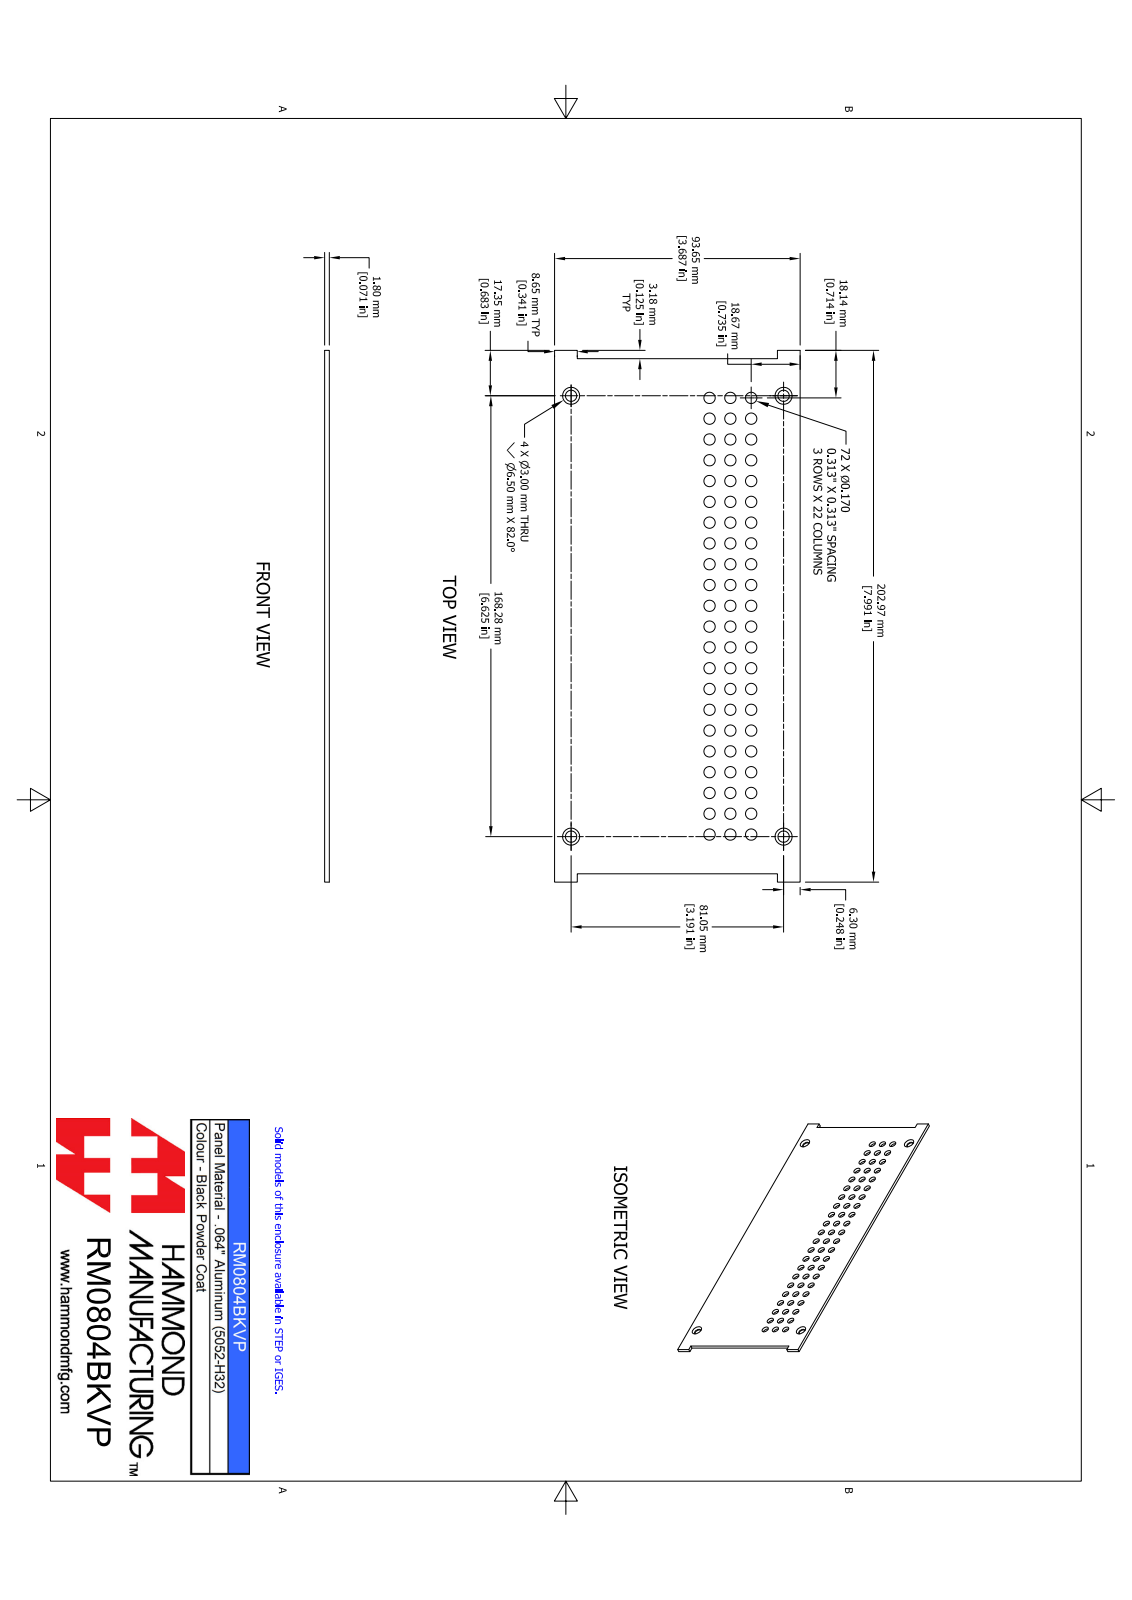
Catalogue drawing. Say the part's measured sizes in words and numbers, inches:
The part is named "RM0804BKVP". Its 3-D file was written by "SolidWorks 2021 (AUTOMOTIVE_DESIGN)". It is 1 solid with 88 faces: 14 planar, 70 cylindrical and 4 other. Overall it measures 7.991 by 3.687 by 0.071 inches. Its volume is 1.919 cubic inches and its surface area 58.54 square inches. Round holes: 66 of diameter 0.17, 4 of diameter 0.169. The main face-to-face distances are 0.071, 3.687, 7.741, 0.125, 7.866, 7.991, 0.341, 3.346, 0.341, 3.006. The hole center spacings are 0.699, 0.313, 0.442, 0.988, 1.289, 0.625, 0.937, 1.25.
